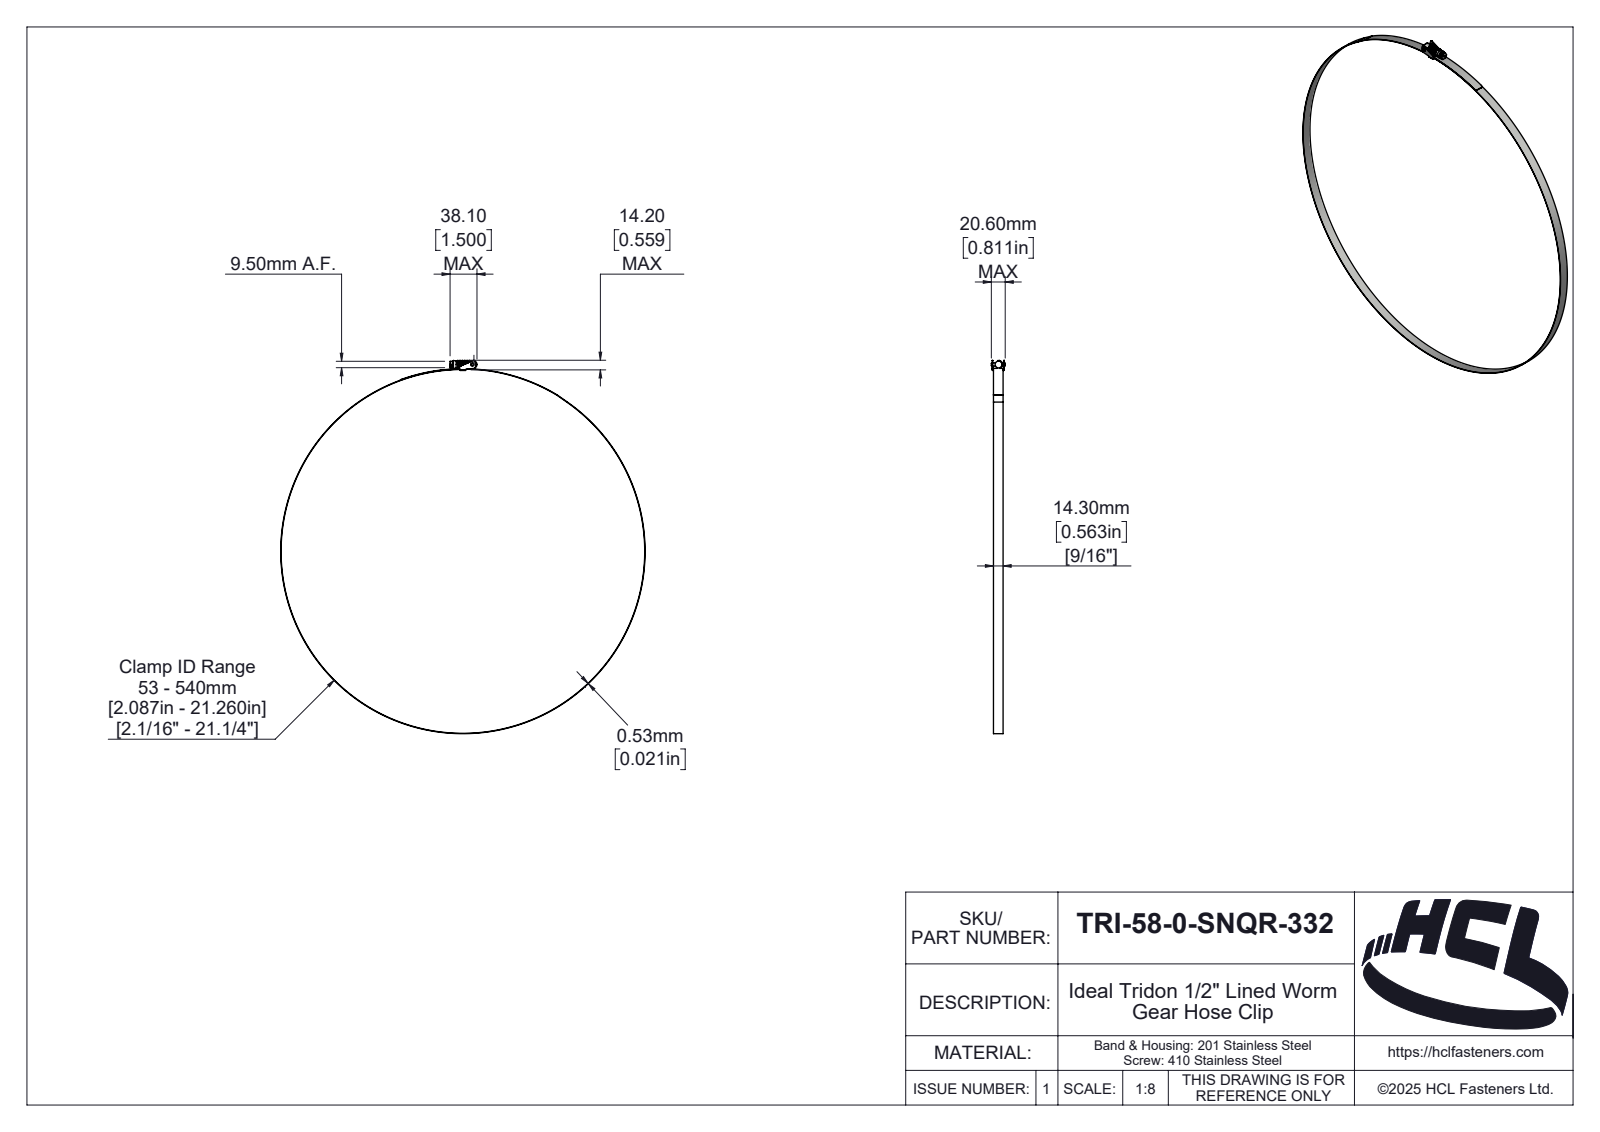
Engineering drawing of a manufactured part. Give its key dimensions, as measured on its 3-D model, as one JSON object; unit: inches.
{"part_name": "TRI-58-0-SNQR-332", "step_written_by": "SolidWorks 2025 (AUTOMOTIVE_DESIGN)", "units": "inches", "bodies": {"solids": 5, "faces": 222, "planar": 44, "cylindrical": 112, "other": 66}, "overall_size": [21.812, 21.302, 0.811], "volume_in3": 1.062, "surface_area_in2": 88.55, "round_holes": [[0.197, 1], [21.26, 1]], "round_bosses_or_shafts": [[21.302, 1], [0.398, 1]], "partial_cylinders_radius": [[0.039, 11], [0.004, 2], [0.035, 2], [0.118, 2], [0.018, 1], [0.074, 1], [0.079, 1], [0.093, 1]], "face_to_face_distances": [0.563, 0.031, 0.677, 0.073, 0.636, 0.041, 0.604, 0.021, 0.709, 0.646], "hole_center_spacings": [10.935]}
